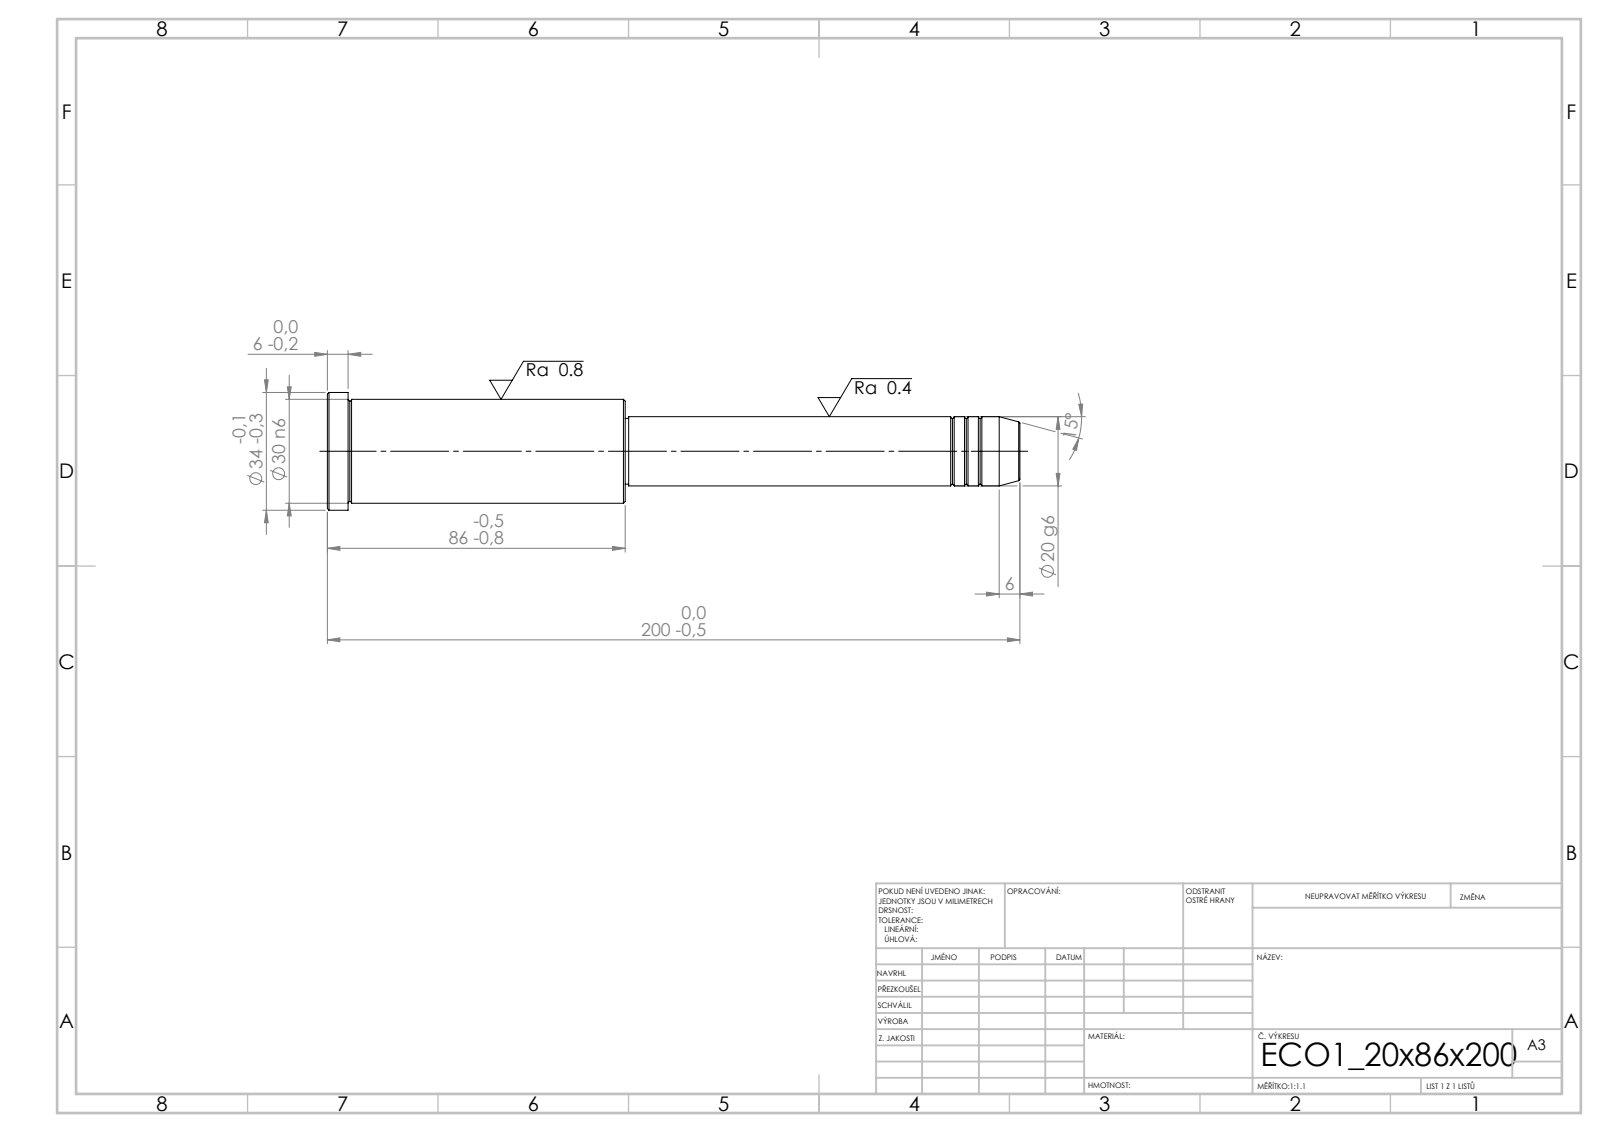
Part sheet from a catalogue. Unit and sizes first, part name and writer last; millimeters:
Units: millimetres
Overall size (bounding box): 200 × 34 × 34
Round bosses / shafts (diameter × count): ⌀34 ×1, ⌀30 ×1, ⌀20 ×1, ⌀19 ×1
Main face-to-face distances: 86, 114, 200, 194, 80, 6, 113, 1, 81, 87
Volume: 97 358 mm³ · Surface area: 17 190 mm²
Bodies: 1 solid, 43 faces (5 planar, 14 cylindrical, 24 other)
STEP written by: SolidWorks 2019 (CONFIG_CONTROL_DESIGN)
